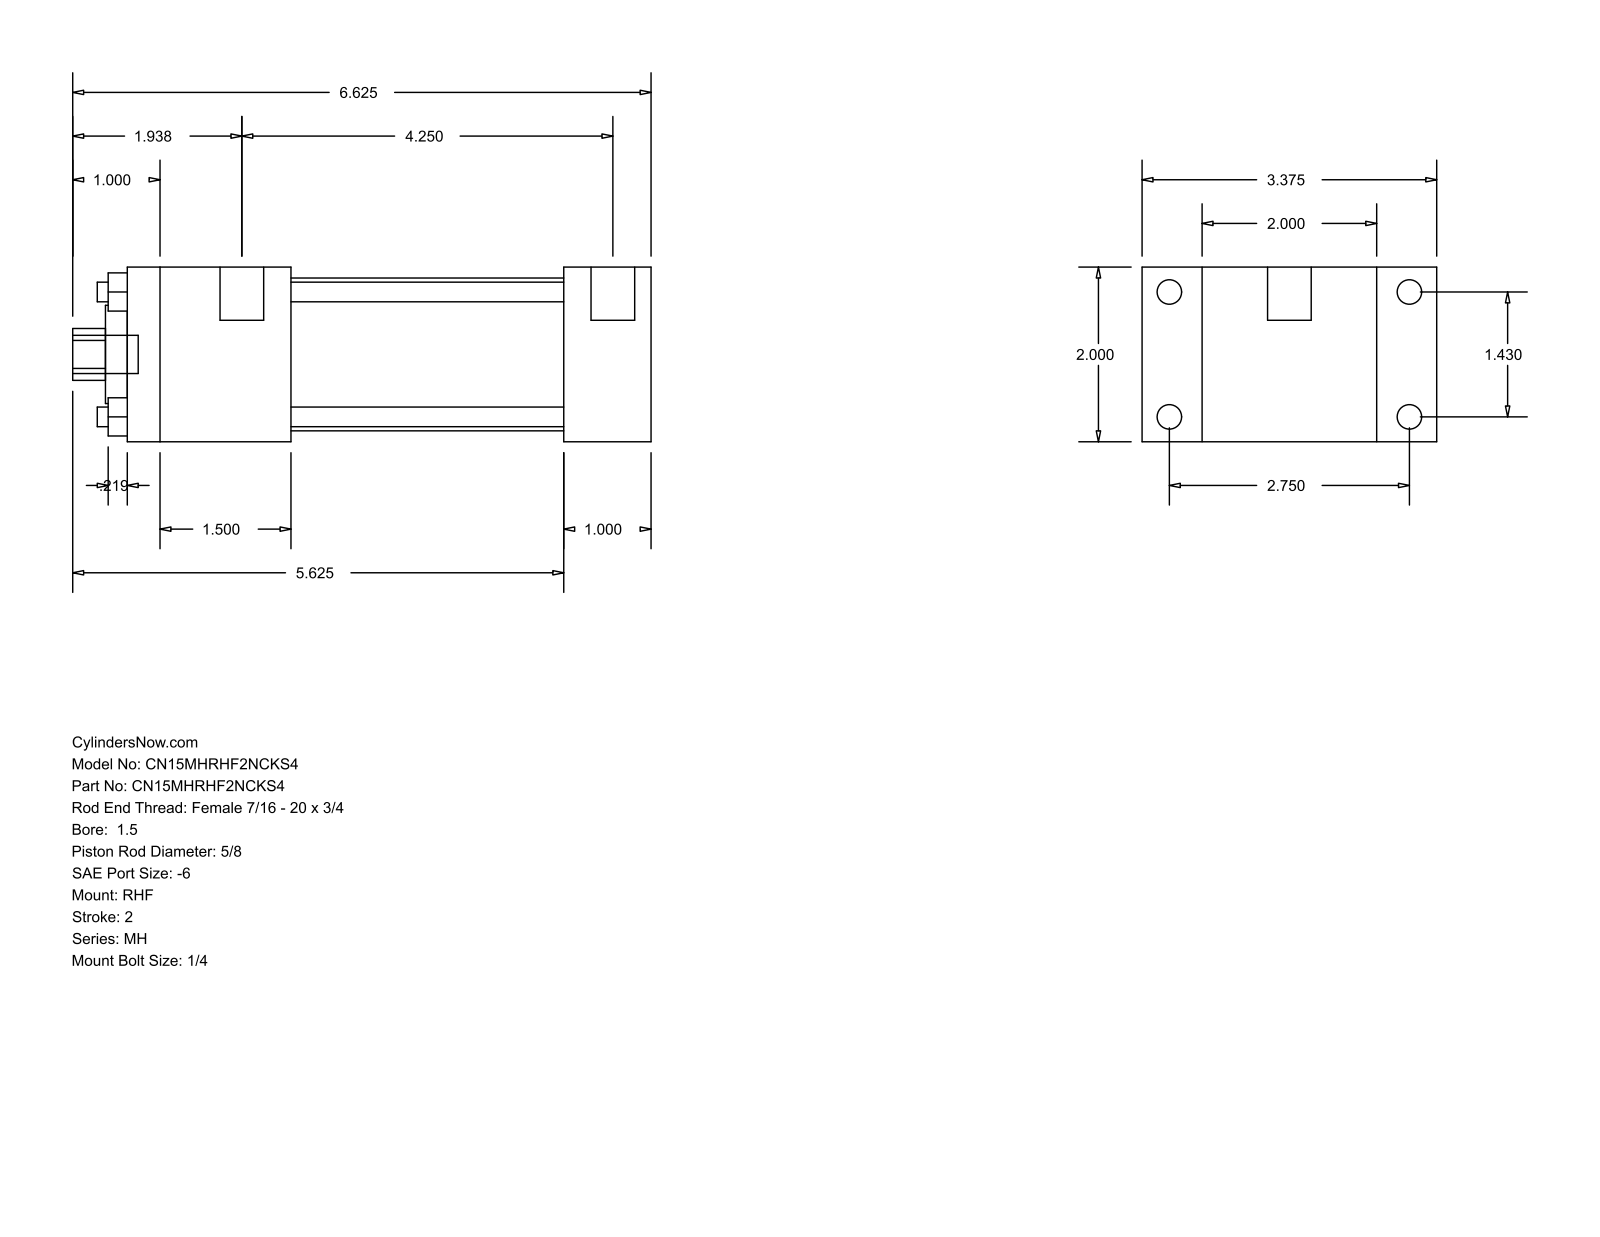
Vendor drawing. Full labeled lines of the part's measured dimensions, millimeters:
Part name (STEP PRODUCT): MH_RHF__0150_0.625
STEP written by: GSSL Pune (CONFIG_CONTROL_DESIGN)
Units: millimetres
Bodies: 0 solids, 88 faces (60 planar, 28 cylindrical, 0 other)
Overall size (bounding box): 168.28 × 85.72 × 50.8
Round holes (diameter × count): ⌀5.71 ×4, ⌀15.88 ×1, ⌀28.57 ×1, ⌀44.45 ×1
Round bosses / shafts (diameter × count): ⌀7.14 ×4, ⌀5.56 ×4, ⌀12.7 ×2, ⌀11.11 ×1
Partial cylindrical surfaces — rounded edges, fillets, slot ends (radius × count): R7.54 ×1
Main face-to-face distances: 50.8, 17.46, 68.26, 25.4, 127, 152.4, 85.72, 47.62, 79.38, 104.78
Hole centre spacings: 25.68, 36.32, 51.36
